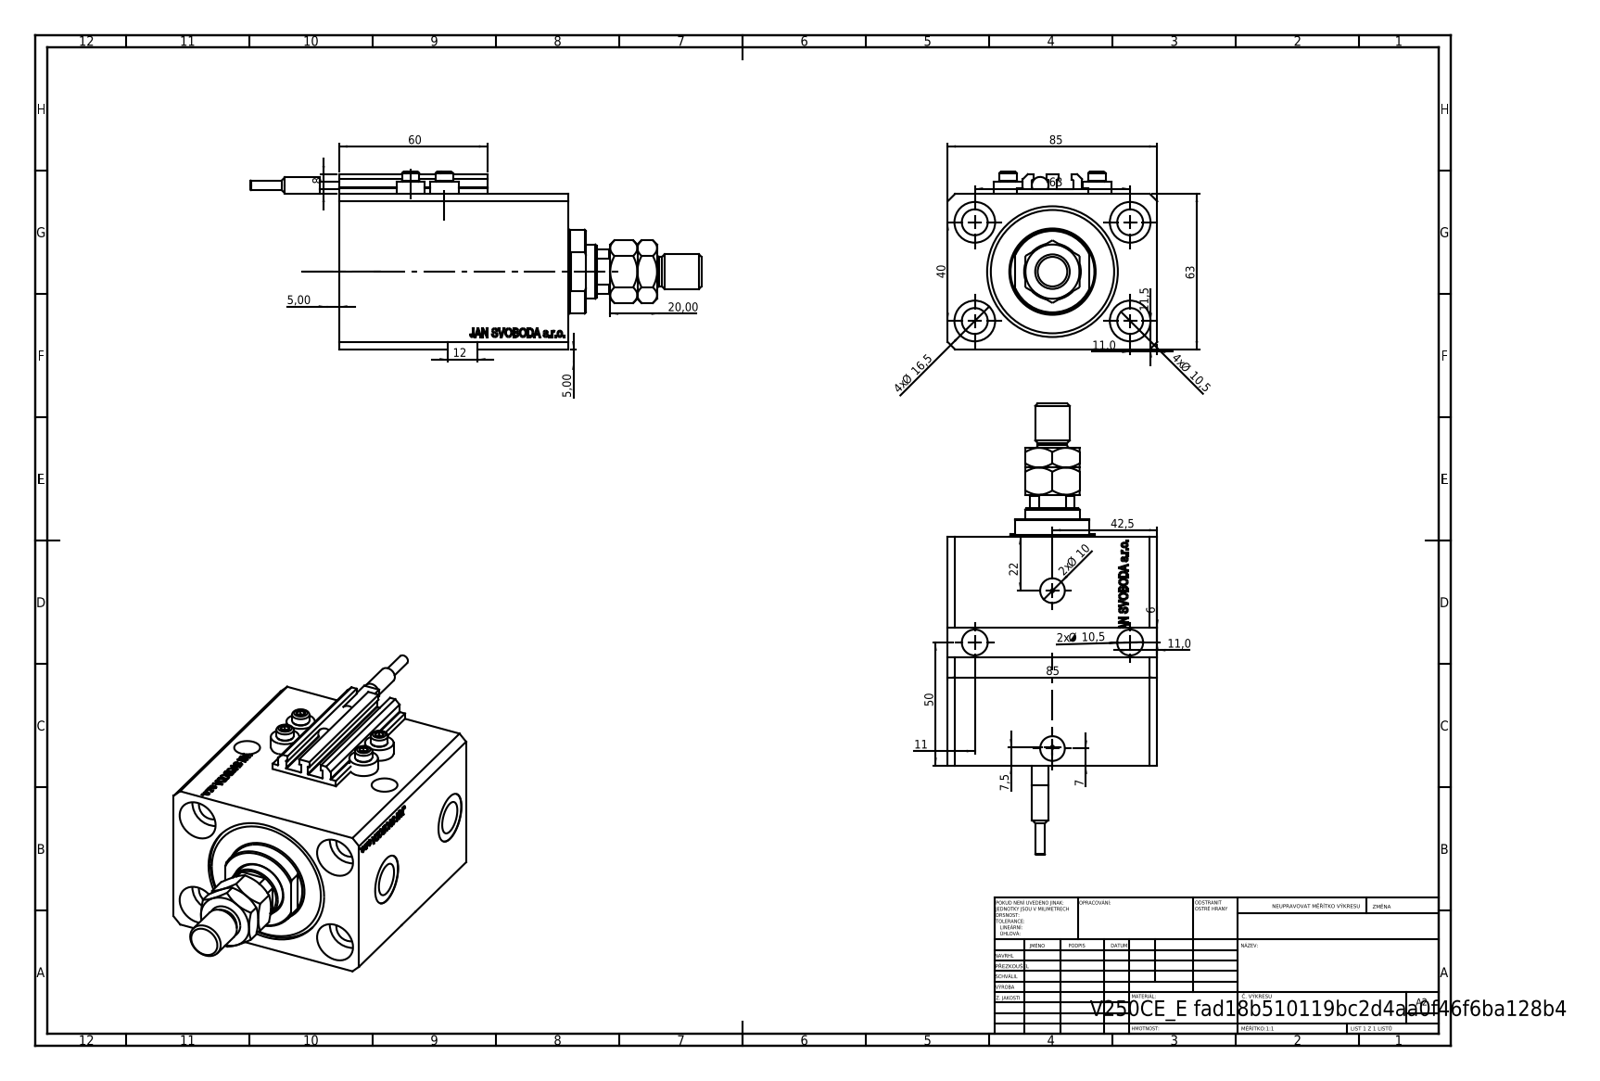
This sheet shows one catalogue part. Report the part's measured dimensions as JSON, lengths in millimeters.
{"part_name": "MTA; V250CE_E; V250CE_C_VCP; ALLEN BOLT V250CE (+2 more)", "step_written_by": "SolidWorks 2019 (CONFIG_CONTROL_DESIGN)", "units": "millimeters", "bodies": {"solids": 10, "faces": 1162, "planar": 566, "cylindrical": 136, "other": 460}, "overall_size": [182.9, 85, 72], "volume_mm3": 449557, "surface_area_mm2": 102367, "round_holes": [[10.5, 6], [1.25, 4], [4, 4], [16.5, 4], [10, 2], [13.16, 2], [20, 2], [12.5, 1], [22, 1], [40, 1], [53, 1]], "round_bosses_or_shafts": [[11.6, 4], [7, 4], [34, 1], [14, 1], [12, 1], [6.8, 1], [6.5, 1], [4, 1]], "partial_cylinders_radius": [[0.2, 10], [10.5, 1]], "face_to_face_distances": [63, 85, 93, 65.9, 54.5, 27.1, 11.4, 81.6, 3, 65], "hole_center_spacings": [37.31, 63, 13.6, 15.4, 24.96, 28.02, 28.43, 33.62]}
